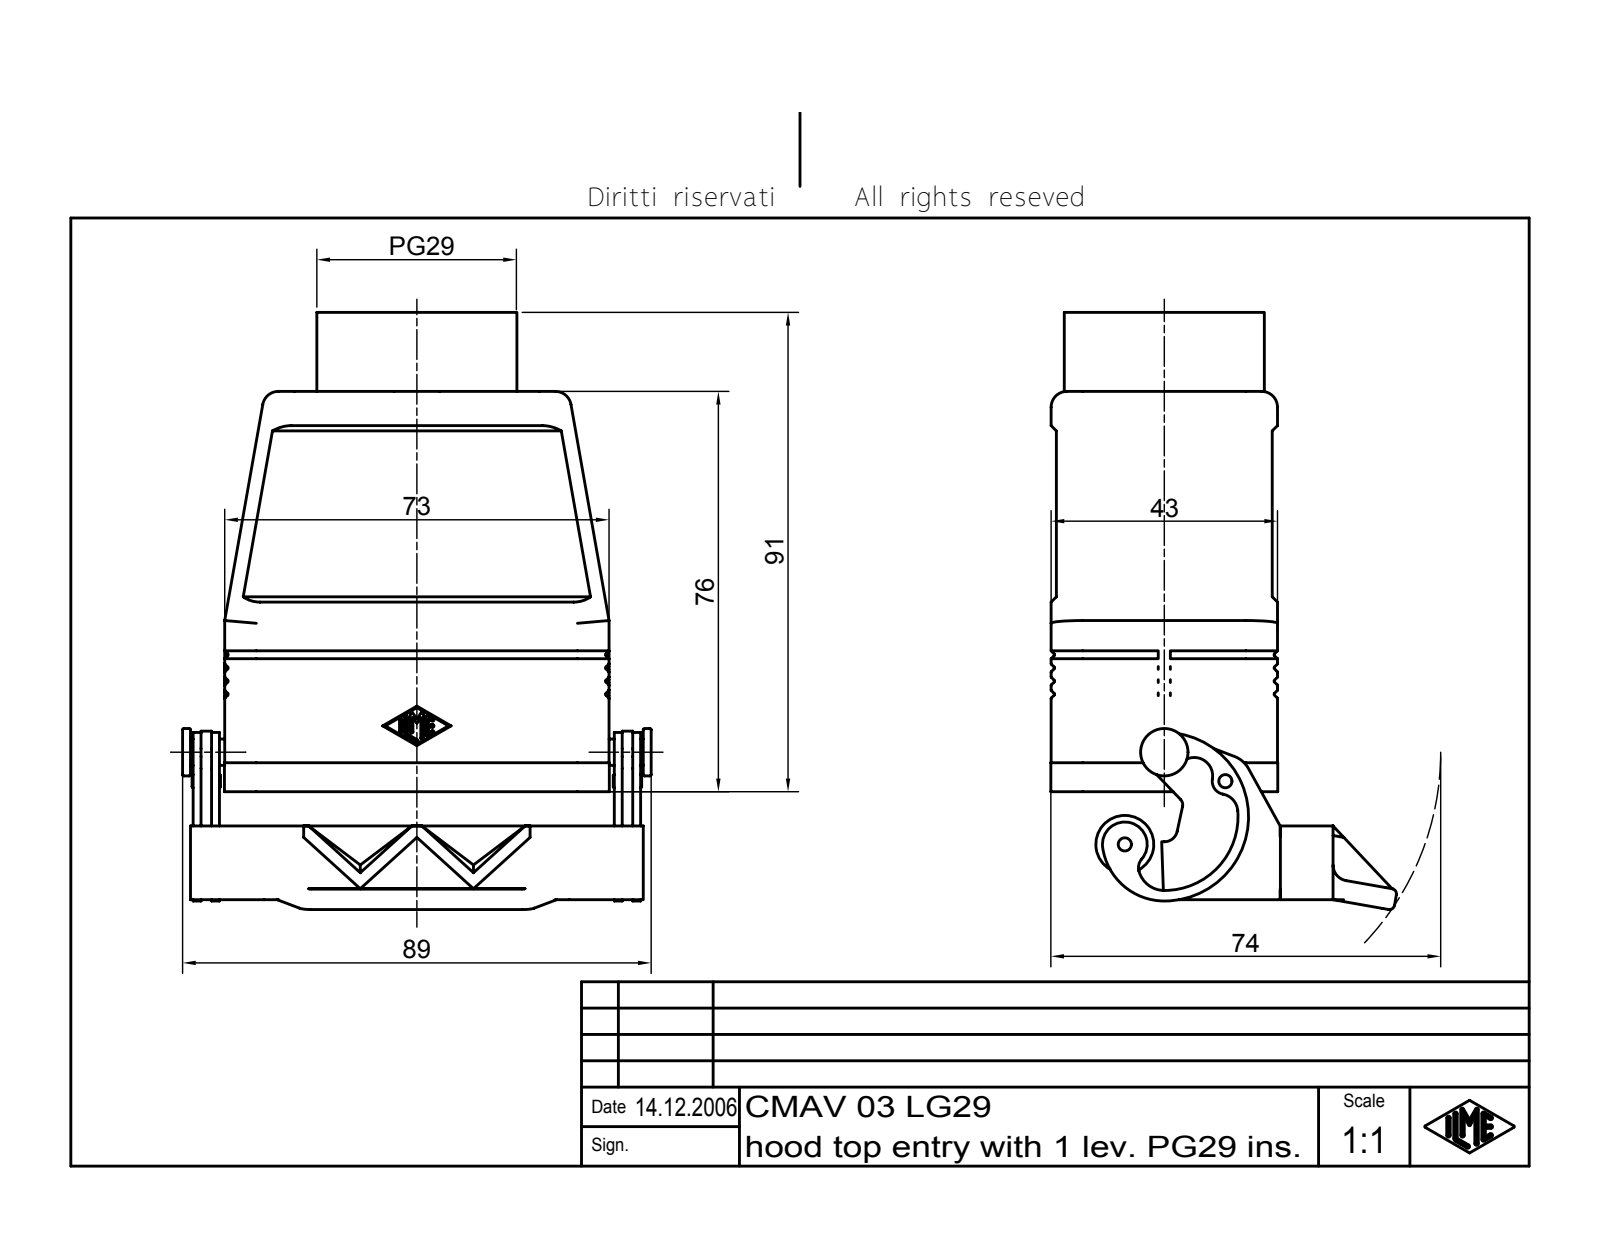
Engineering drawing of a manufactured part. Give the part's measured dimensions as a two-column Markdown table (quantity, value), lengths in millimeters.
| quantity | value |
| --- | --- |
| part name | CMAV 03 LG29 |
| STEP written by | Autodesk Inventor 7 (AUTOMOTIVE_DESIGN) |
| units | millimeters |
| bodies | 1 solid, 847 faces (192 planar, 300 cylindrical, 355 other) |
| overall size | 113.37 × 89 × 65.64 |
| volume | 78 647 mm³ |
| surface area | 48 406 mm² |
| round holes (diameter × count) | 2.5 × 1, 33.48 × 1, 35.48 × 1 |
| round bosses / shafts (diameter × count) | 38 × 1, 11 × 1, 9 × 1, 5 × 1, 3.1 × 1, 2 × 1 |
| partial cylindrical surfaces (radius × count) | 0.2 × 52, 0.25 × 26, 2.5 × 11, 6 × 8, 3 × 7, 1 × 6, 2.45 × 4, 6.05 × 4 |
| main face-to-face distances | 3.45, 3.5, 39.55, 39.5, 36.05, 36, 2.45, 3.55, 36.1, 2.5 |
